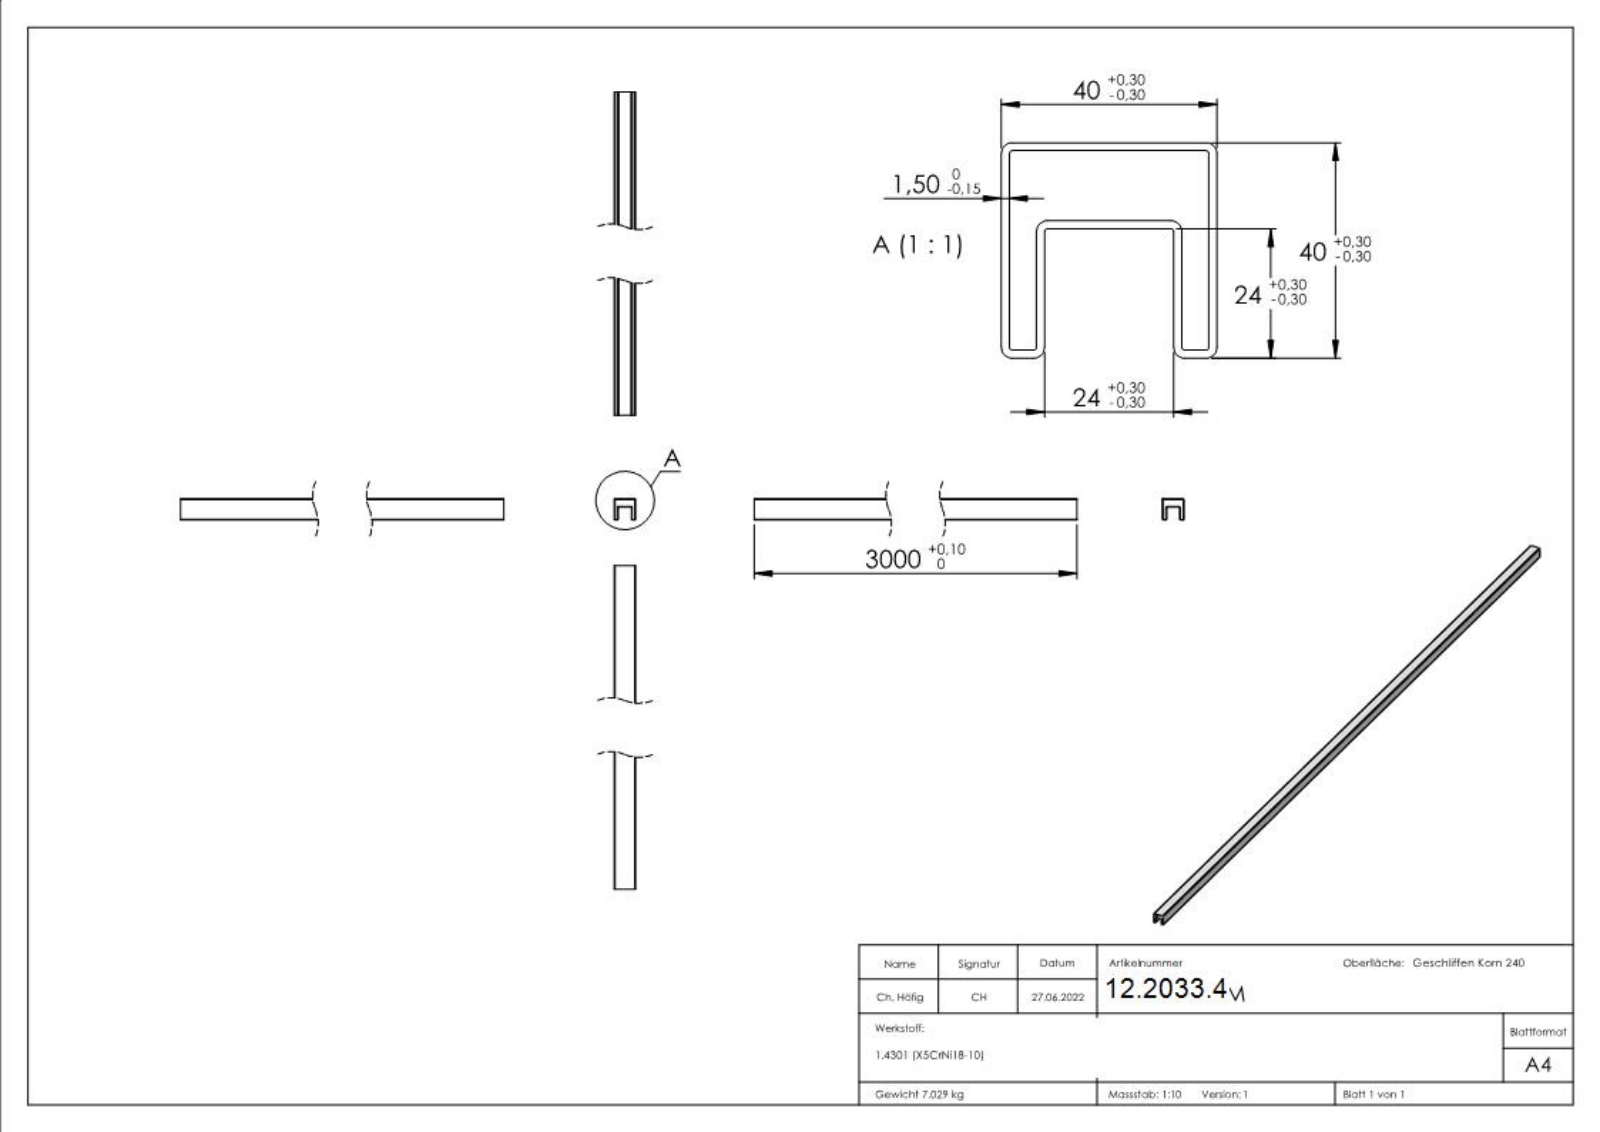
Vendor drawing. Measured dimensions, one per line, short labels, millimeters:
name: 60337-2403M
written by: SolidWorks 2018 (CONFIG_CONTROL_DESIGN)
unit: mm
bodies: 1 solid, 334 faces (175 planar, 16 cylindrical, 143 other)
size: 3000 × 40 × 40
volume: 889 685 mm³; area: 1 187 000 mm²
rounds: 8× R0.5, 8× R2
face distances: 1.5, 38.5, 6.5, 32, 25.5, 14.5, 40, 37, 33.5, 5
